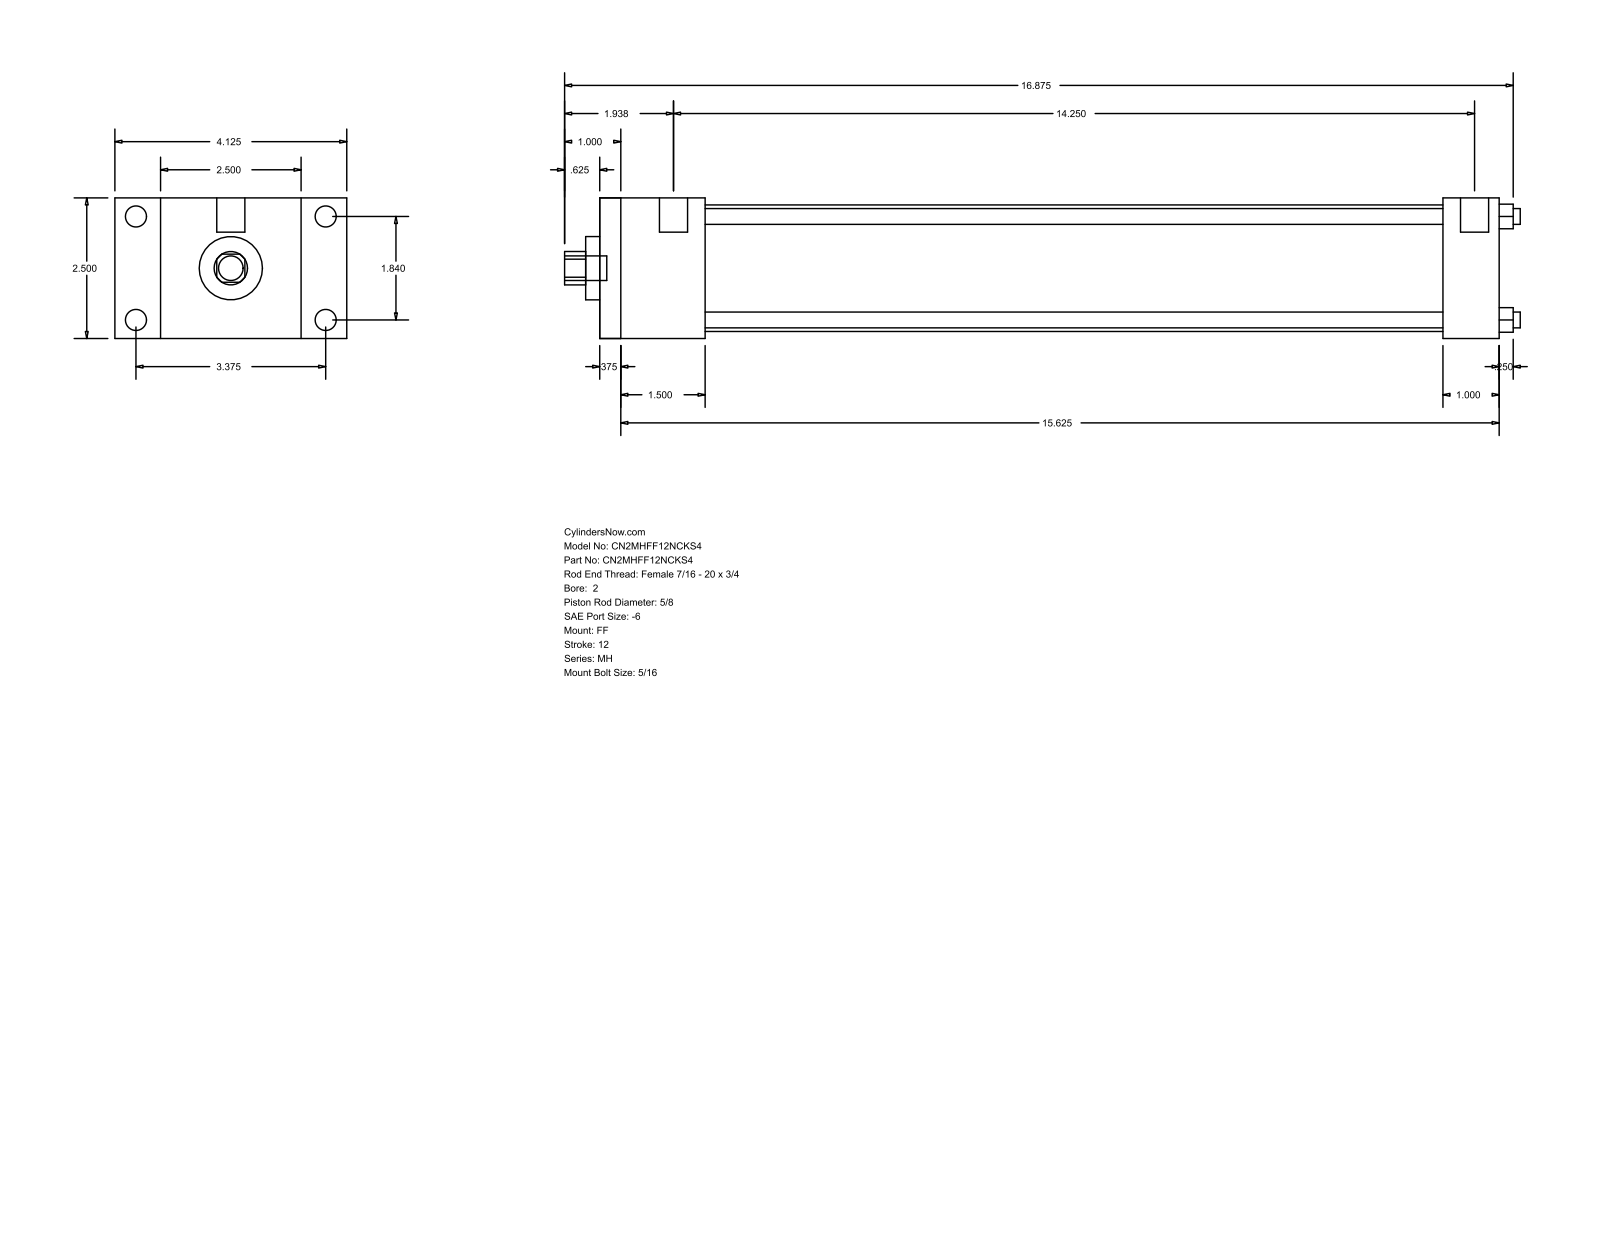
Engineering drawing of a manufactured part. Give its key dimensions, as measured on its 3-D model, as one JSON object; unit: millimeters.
{"part_name": "MH_FF__0200_0.625", "step_written_by": "GSSL Pune (CONFIG_CONTROL_DESIGN)", "units": "millimeters", "bodies": {"solids": 0, "faces": 92, "planar": 64, "cylindrical": 28, "other": 0}, "overall_size": [431.8, 104.78, 63.5], "round_holes": [[7.14, 4], [15.88, 1], [28.57, 1], [57.15, 1]], "round_bosses_or_shafts": [[9.53, 4], [5.56, 4], [12.7, 2], [11.11, 1]], "partial_cylinders_radius": [[7.54, 1]], "face_to_face_distances": [63.5, 406.39, 9.52, 396.87, 38.1, 47.62, 381, 371.48, 333.38, 358.77], "hole_center_spacings": [33.05, 46.74, 66.1]}
